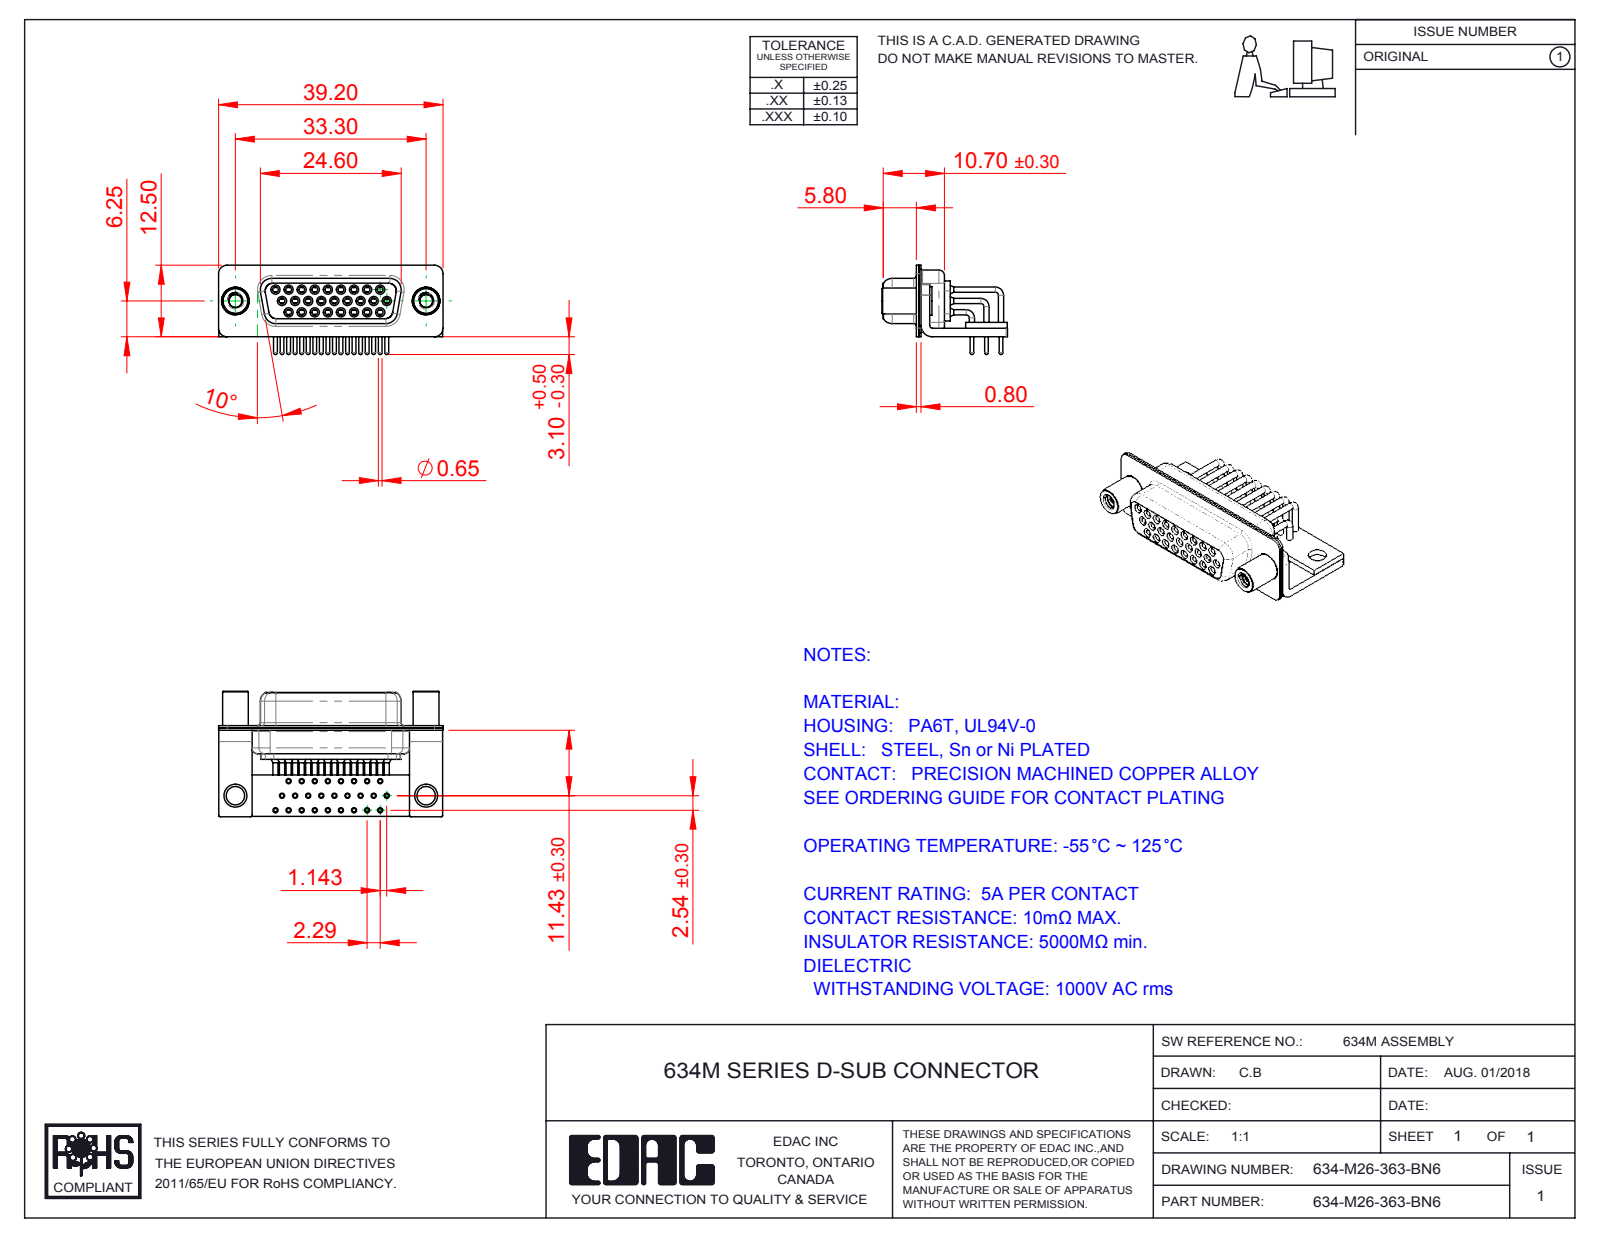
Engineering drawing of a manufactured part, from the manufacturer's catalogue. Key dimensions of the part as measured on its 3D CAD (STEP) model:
Part name (STEP PRODUCT): 634M Contact Row 3; 634M Housing_26 Contacts; 634-M26-363-BN6; 634M Shell Front_26 Contacts (+6 more)
STEP written by: SolidWorks 2016 (CONFIG_CONTROL_DESIGN)
Units: millimetres
Bodies: 34 solids, 1809 faces (485 planar, 851 cylindrical, 473 other)
Overall size (bounding box): 39.2 × 21.9 × 15.6
Volume: 3 190 mm³ · Surface area: 10 090 mm²
Round holes (diameter × count): ⌀0.9 ×26, ⌀1 ×26, ⌀1.1 ×26, ⌀1.7 ×26, ⌀1.8 ×26, ⌀2 ×26, ⌀2.26 ×2, ⌀3.2 ×2, ⌀4 ×2, ⌀4.8 ×2
Round bosses / shafts (diameter × count): ⌀0.9 ×27, ⌀1.6 ×26, ⌀1.5 ×26, ⌀0.65 ×26, ⌀5 ×2, ⌀4.9 ×2, ⌀4.5 ×2, ⌀2 ×1
Partial cylindrical surfaces — rounded edges, fillets, slot ends (radius × count): R0.25 ×16, R1.5 ×16, R2 ×13, R1.35 ×8, R1.6 ×8, R0.5 ×5, R0.6 ×4, R0.65 ×4
Main face-to-face distances: 0.4, 2.3, 1.9, 0.8, 1, 1.5, 9.35, 8.5, 1.45, 8.95
Hole centre spacings: 4.57, 2.29, 2.28, 3.96, 6.05, 6.86, 4.27, 2.78
